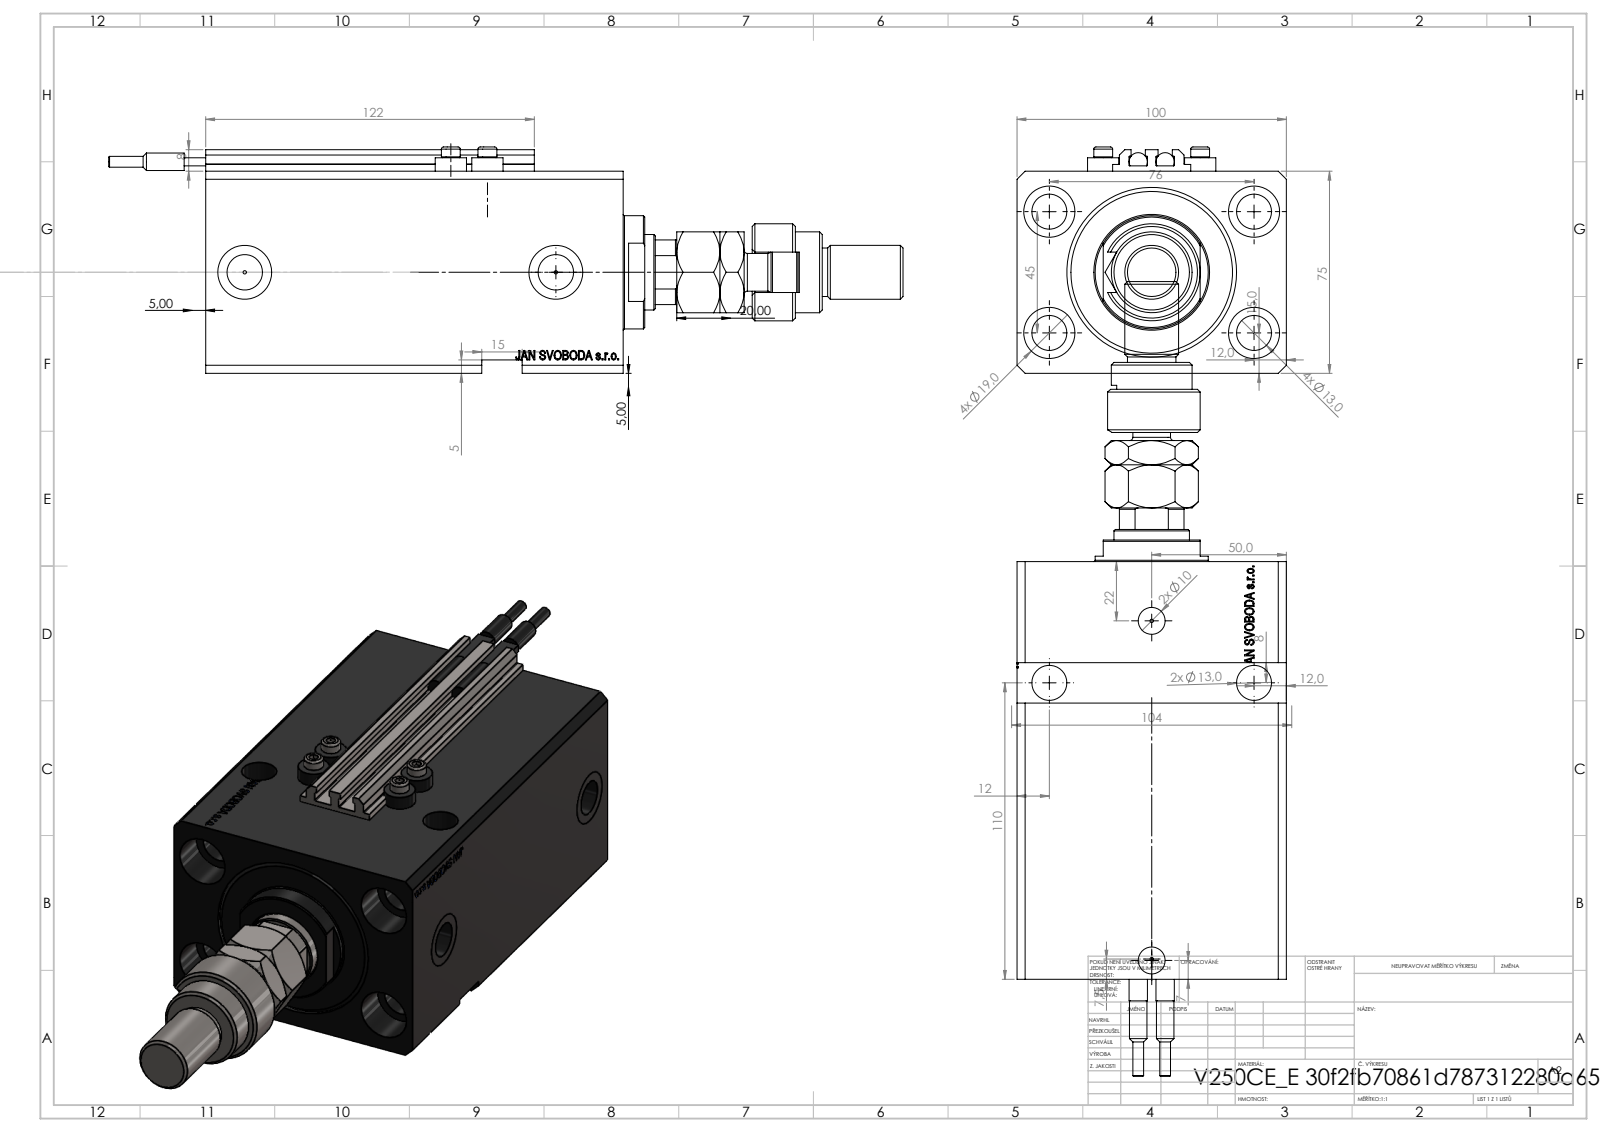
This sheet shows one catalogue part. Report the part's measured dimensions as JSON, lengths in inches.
{"part_name": "MFA; V250CE_VC_E; V250CE_C_VCP; ALLEN BOLT V250CE (+3 more)", "step_written_by": "SolidWorks 2019 (CONFIG_CONTROL_DESIGN)", "units": "inches", "bodies": {"solids": 12, "faces": 1241, "planar": 599, "cylindrical": 163, "other": 479}, "overall_size": [11.61, 3.937, 3.307], "volume_in3": 61.27, "surface_area_in2": 297.3, "round_holes": [[0.512, 6], [0.049, 4], [0.157, 4], [0.748, 4], [0.394, 2], [0.518, 2], [0.787, 2], [0.728, 1], [1.102, 1], [1.969, 1], [2.48, 1]], "round_bosses_or_shafts": [[0.457, 4], [0.276, 4], [0.268, 2], [0.256, 2], [0.157, 2], [1.654, 1], [1.417, 1], [1.181, 1]], "partial_cylinders_radius": [[0.008, 10], [0.295, 1], [0.472, 1], [0.531, 1]], "face_to_face_distances": [2.953, 3.937, 6.102, 0.469, 5.634, 5.055, 4.587, 1.047, 0.394, 1.906], "hole_center_spacings": [1.739, 2.992, 0.535, 0.816, 1.086, 1.324, 1.417, 1.515]}
